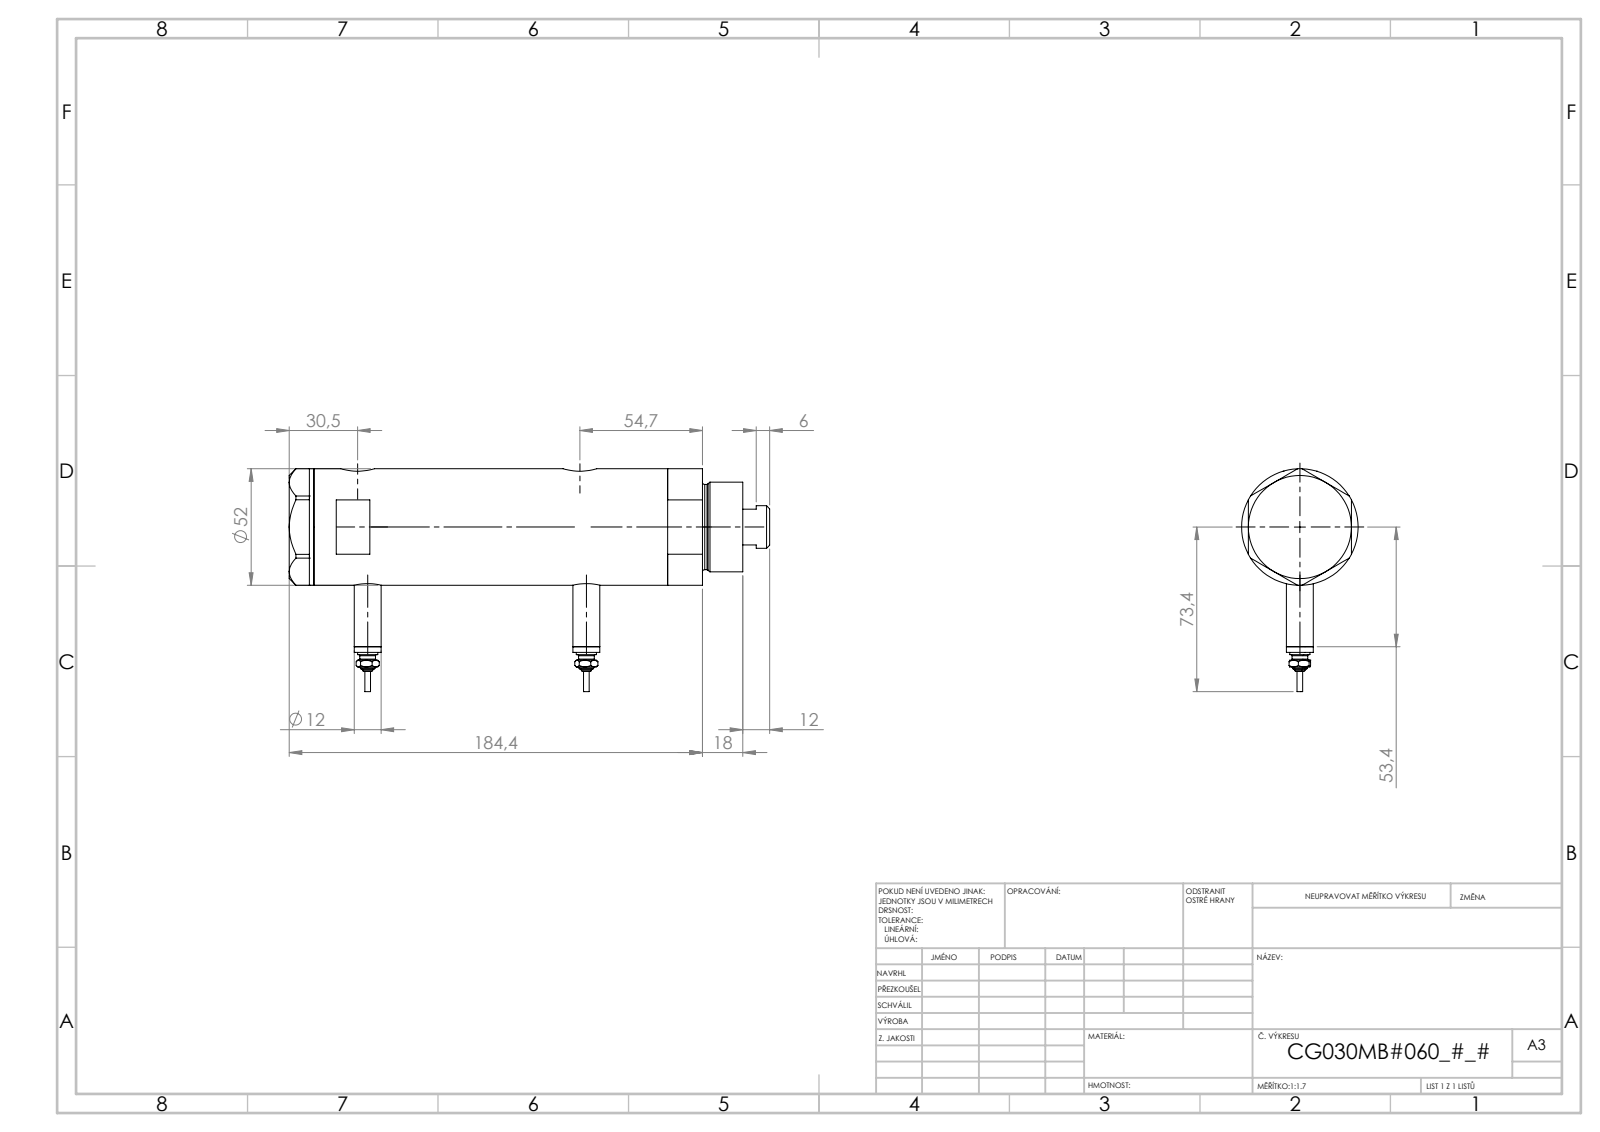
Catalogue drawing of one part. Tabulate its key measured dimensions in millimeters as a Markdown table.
| quantity | value |
| --- | --- |
| part name | V270CG_BACK; V270CG_FRONT; V270CG_VC; Switch (+1 more) |
| STEP written by | SolidWorks 2019 (CONFIG_CONTROL_DESIGN) |
| units | millimeters |
| bodies | 6 solids, 226 faces (93 planar, 69 cylindrical, 64 other) |
| overall size | 214.4 × 99.4 × 52 |
| volume | 392 865 mm³ |
| surface area | 89 526 mm² |
| round holes (diameter × count) | 9.73 × 2, 12.5 × 2, 15 × 2, 6.5 × 1, 20 × 1, 21.5 × 1, 30 × 1, 33 × 1, 44 × 1 |
| round bosses / shafts (diameter × count) | 12 × 2, 9 × 2, 7 × 2, 4.5 × 2, 2.5 × 2, 52 × 1, 40 × 1, 38 × 1 |
| main face-to-face distances | 121.5, 23.8, 97.7, 11, 34.8, 132.5, 46, 36.4, 168.9, 157.9 |
| hole center spacings | 2.9, 4.5, 94.7, 97.6, 99.2, 102.1 |
